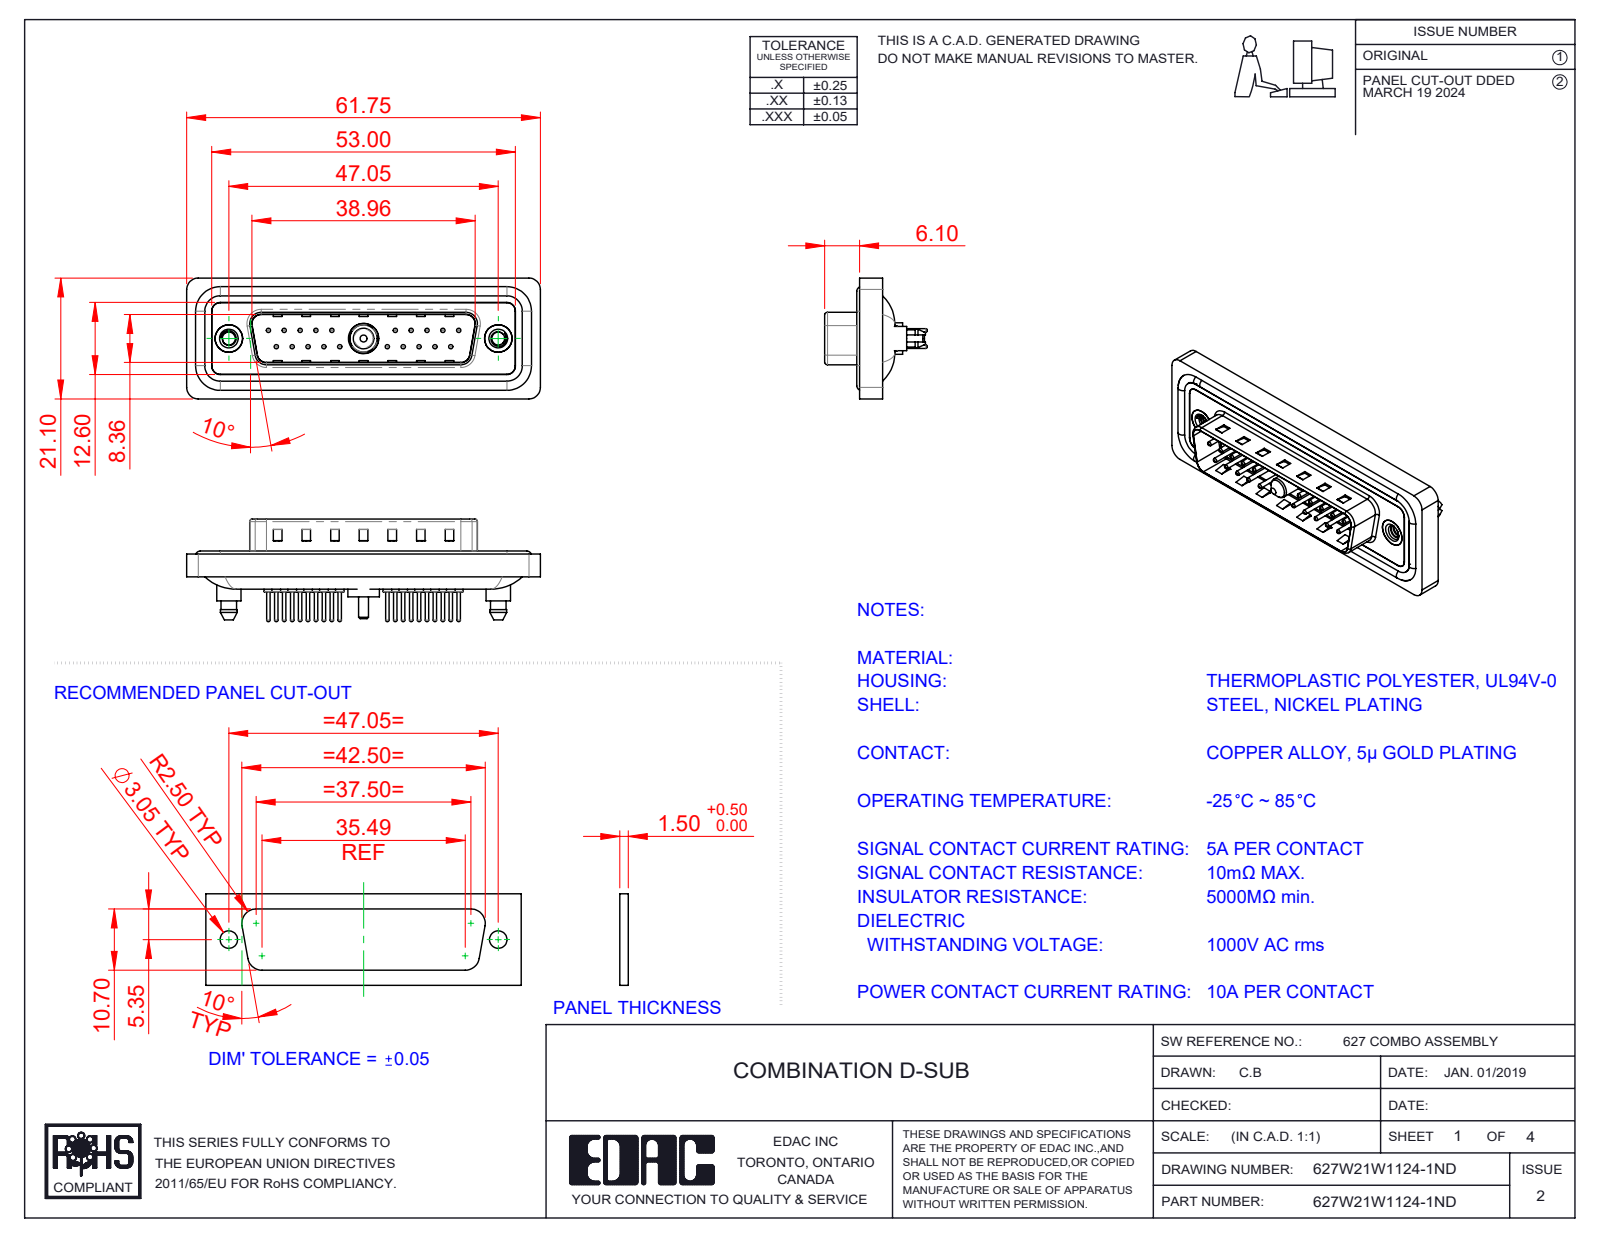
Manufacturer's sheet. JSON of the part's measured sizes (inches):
{"part_name": "627W21W1124-1ND; 627Combo Shell Rear_25 Contacts; 627Combo Shell Front_25 Contacts; 627Combo Waterproof Housing_25 Contacts (+6 more)", "step_written_by": "SolidWorks 2023 (CONFIG_CONTROL_DESIGN)", "units": "inches", "bodies": {"solids": 29, "faces": 1320, "planar": 375, "cylindrical": 527, "other": 418}, "overall_size": [2.431, 0.831, 0.705], "volume_in3": 0.447, "surface_area_in2": 19.03, "round_holes": [[0.03, 20], [0.063, 20], [0.079, 20], [0.089, 2], [0.157, 2], [0.189, 2], [0.197, 2], [0.191, 1], [0.209, 1]], "round_bosses_or_shafts": [[0.059, 20], [0.024, 20], [0.063, 4], [0.213, 2], [0.193, 2], [0.167, 2], [0.217, 1], [0.205, 1]], "partial_cylinders_radius": [[0.059, 24], [0.079, 18], [0.063, 10], [0.02, 8], [0.01, 4], [0.024, 4], [0.026, 4], [0.035, 4]], "face_to_face_distances": [0.016, 0.059, 0.043, 0.063, 0.02, 0.122, 0.114, 0.161, 0.032, 0.377], "hole_center_spacings": [0.124, 0.109, 0.218, 0.327, 0.198, 0.763, 0.826, 0.872]}
